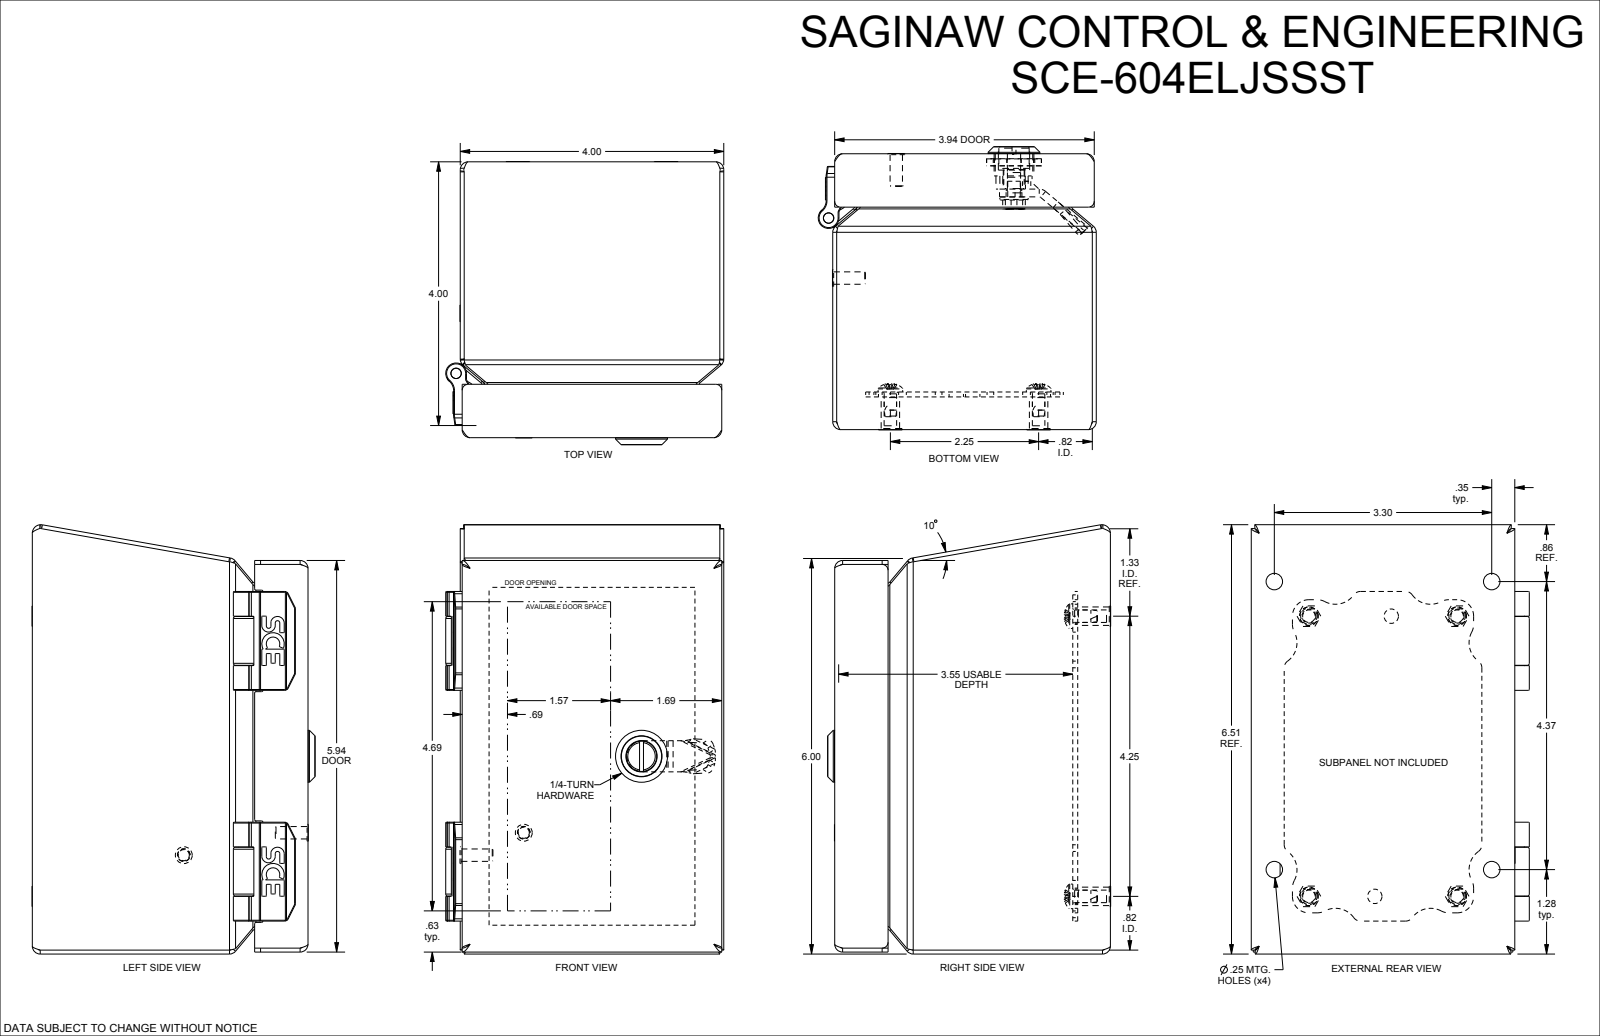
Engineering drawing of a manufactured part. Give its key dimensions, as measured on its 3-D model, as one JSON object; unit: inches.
{"part_name": "SCE-604ELJSSST", "step_written_by": "SolidWorks 2021 (AUTOMOTIVE_DESIGN)", "units": "inches", "bodies": {"solids": 34, "faces": 1454, "planar": 566, "cylindrical": 353, "other": 535}, "overall_size": [6.563, 4.296, 4.22], "volume_in3": 11.77, "surface_area_in2": 365.5, "round_holes": [[0.16, 4], [0.19, 4], [0.25, 4], [0.284, 4], [0.02, 2], [0.1, 2], [0.218, 2], [0.266, 2], [0.158, 1], [0.196, 1], [0.2, 1], [0.239, 1]], "round_bosses_or_shafts": [[0.188, 6], [0.483, 4], [0.373, 4], [0.28, 4], [0.237, 4], [0.16, 4], [0.26, 2], [0.256, 2]], "partial_cylinders_radius": [[0.03, 50], [0.008, 24], [0.013, 21], [0.25, 13], [0.125, 11], [0.01, 10], [0.06, 10], [0.344, 8]], "face_to_face_distances": [0.059, 3.941, 0.06, 4.185, 4.126, 4.125, 4.066, 4, 3.882, 0.571], "hole_center_spacings": [3.5, 0.663, 0.763, 1, 1.25, 2.157, 2.25, 2.804]}
